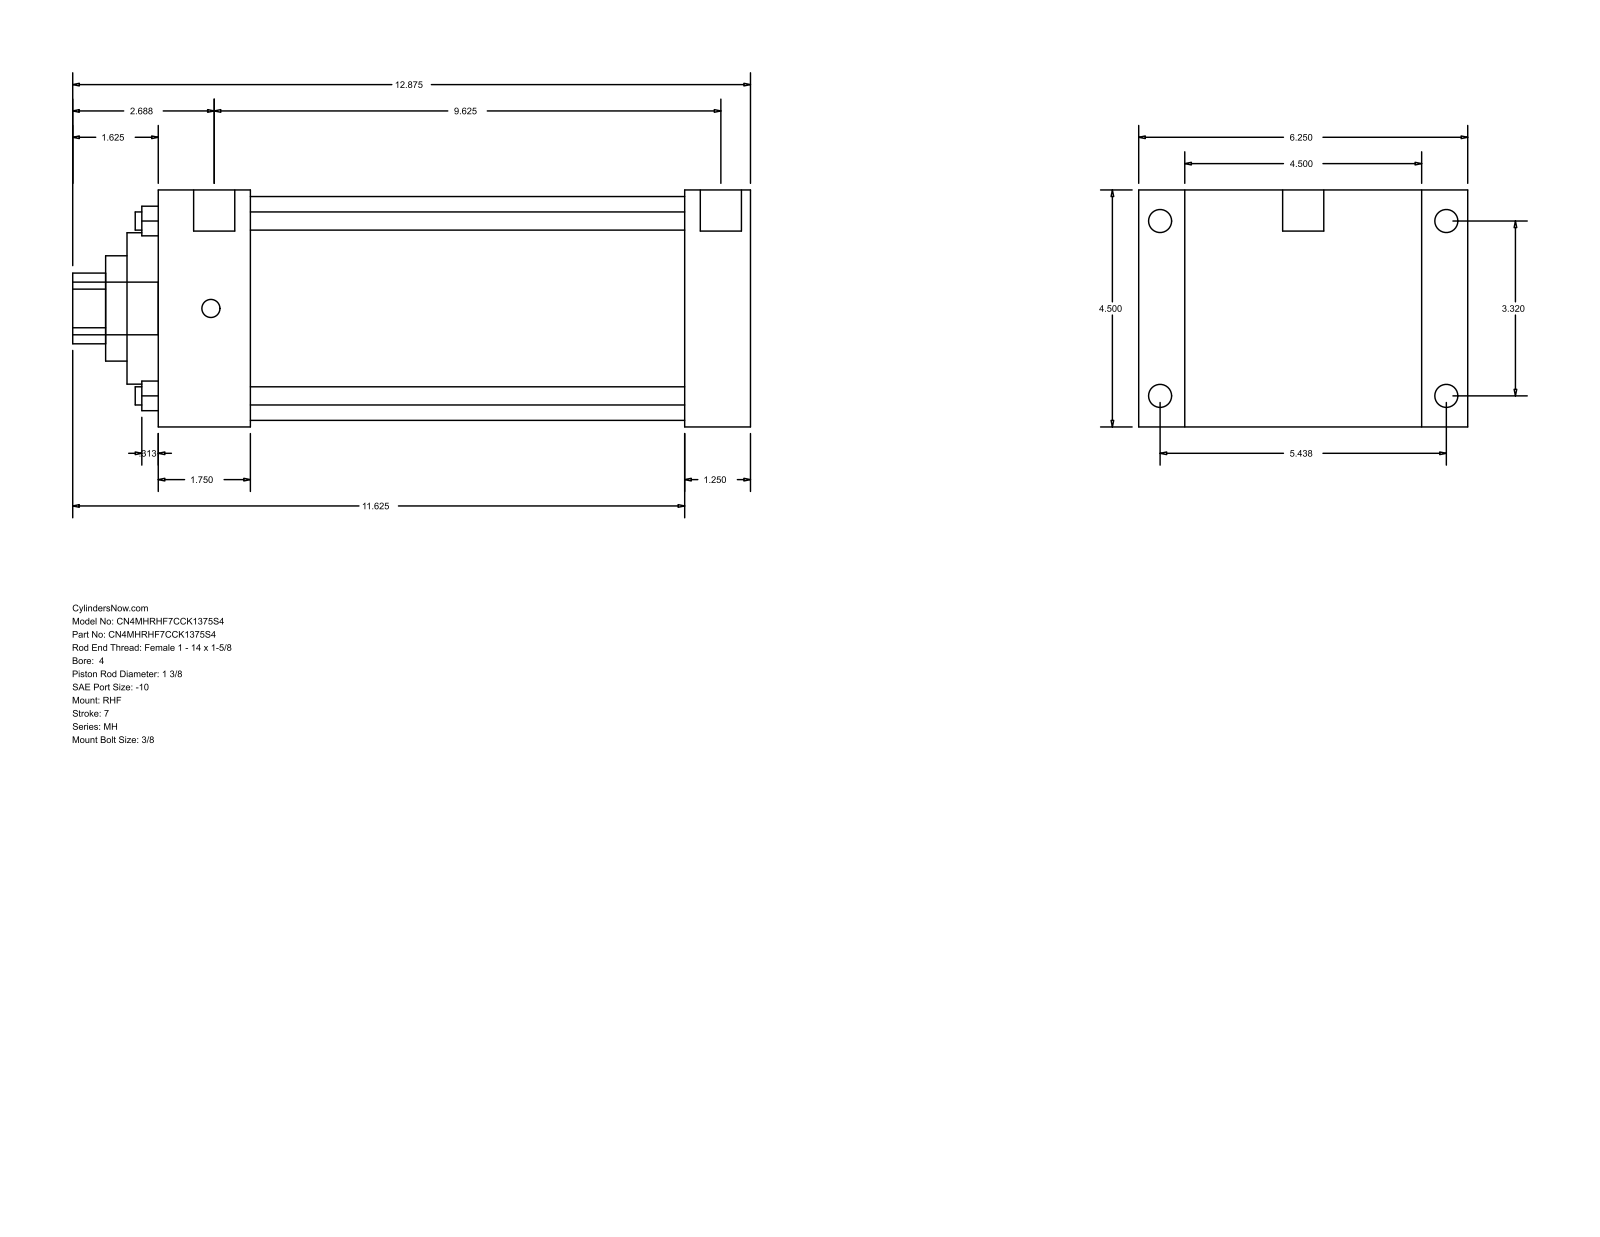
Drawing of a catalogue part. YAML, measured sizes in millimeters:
part_name: "MH_RHF__0400_1.375"
step_written_by: "GSSL Pune (CONFIG_CONTROL_DESIGN)"
units: millimeters
bodies: {solids: 0, faces: 90, planar: 61, cylindrical: 29, other: 0}
overall_size: [327.02, 158.75, 114.3]
round_holes:
  - {diameter: 8.76, count: 4}
  - {diameter: 34.92, count: 1}
  - {diameter: 50.8, count: 1}
  - {diameter: 73.03, count: 1}
  - {diameter: 107.95, count: 1}
round_bosses_or_shafts:
  - {diameter: 11.13, count: 4}
  - {diameter: 8.73, count: 4}
  - {diameter: 19.84, count: 2}
  - {diameter: 25.4, count: 1}
partial_cylinders:
  - {radius: 17.06, count: 1}
face_to_face_distances: [114.3, 285.75, 254, 31.75, 22.23, 136.53, 44.45, 209.55, 241.3, 158.76]
hole_center_spacings: [59.62, 84.32, 119.25]
